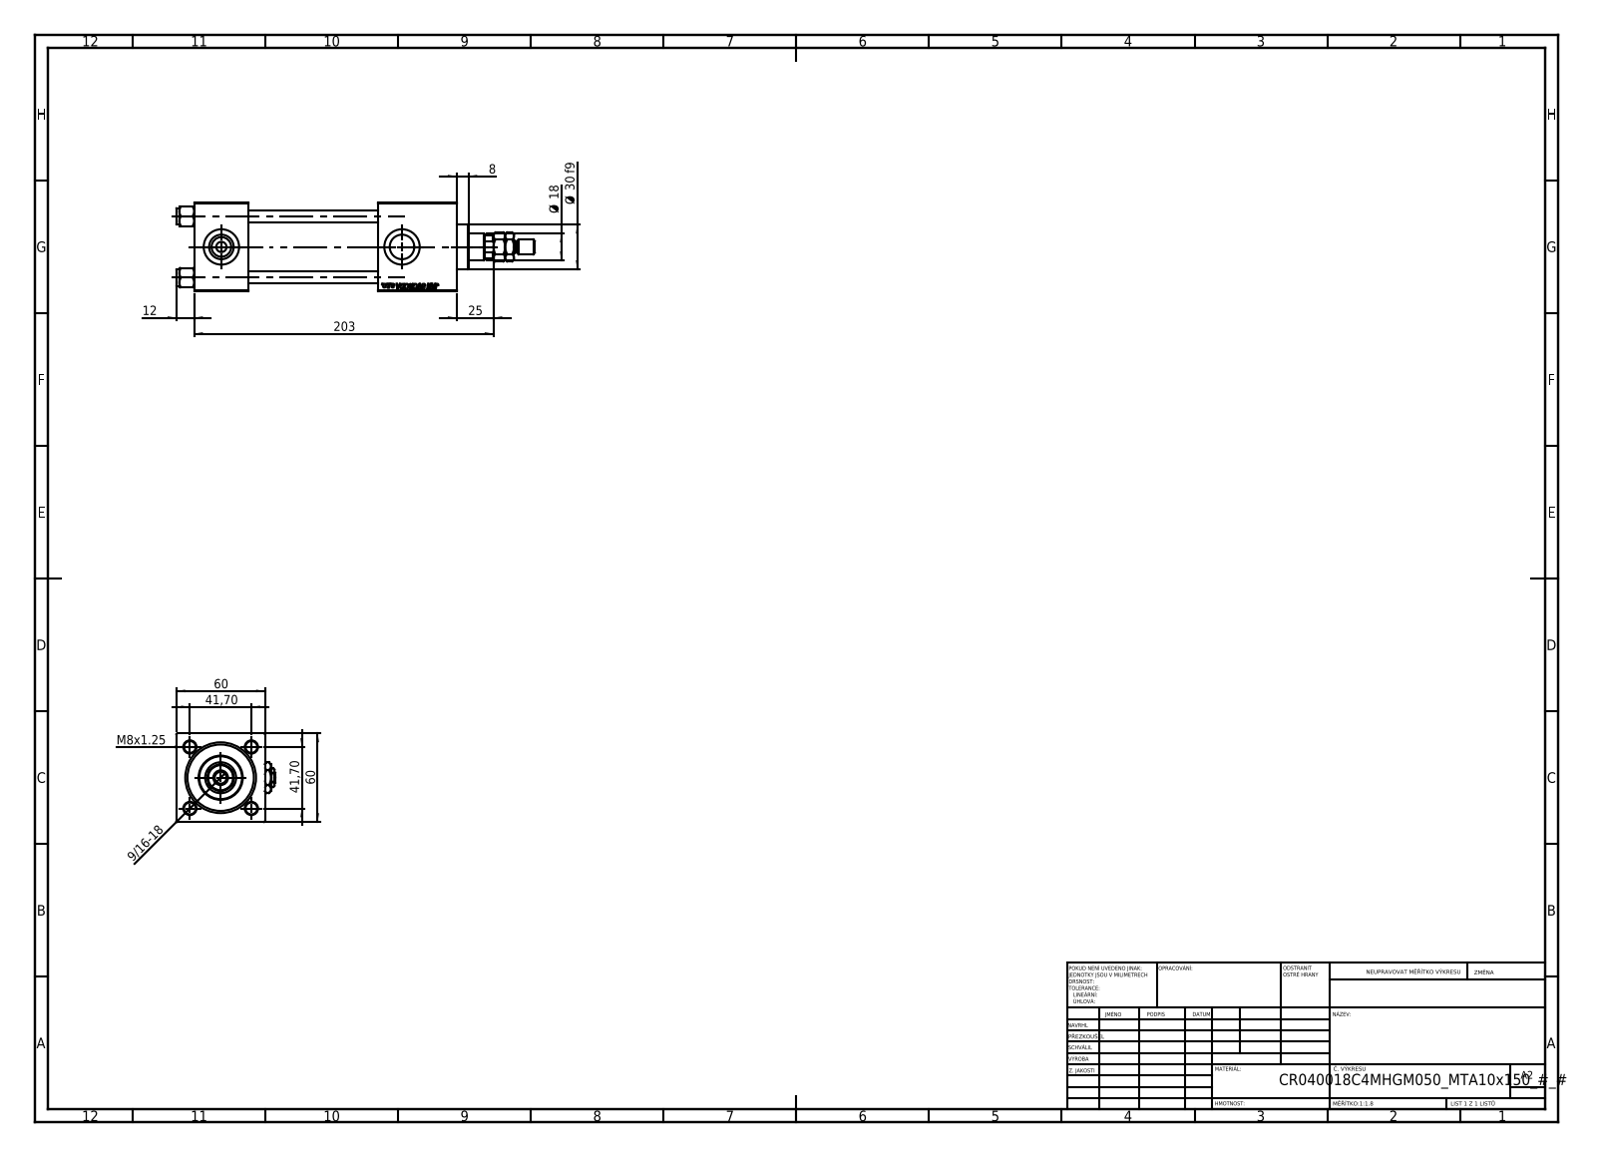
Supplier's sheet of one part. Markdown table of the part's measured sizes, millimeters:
| quantity | value |
| --- | --- |
| part name | V215CR_C_Body; MTA; V215_VC_A; Zatka_pro_OIL_PORT (+3 more) |
| STEP written by | SolidWorks 2019 (CONFIG_CONTROL_DESIGN) |
| units | millimeters |
| bodies | 13 solids, 1245 faces (565 planar, 94 cylindrical, 586 other) |
| overall size | 243 × 67 × 60 |
| volume | 430 988 mm³ |
| surface area | 121 152 mm² |
| round holes (diameter × count) | 8 × 4, 7 × 2, 16.66 × 2, 24 × 2, 8.5 × 1, 18 × 1, 21 × 1, 31 × 1, 40 × 1, 45 × 1 |
| round bosses / shafts (diameter × count) | 11 × 4, 46 × 1, 30 × 1, 10 × 1, 8 × 1 |
| partial cylindrical surfaces (radius × count) | 8.5 × 1 |
| main face-to-face distances | 60, 37, 178, 141, 53, 125, 88, 149.3, 112.3, 24.3 |
| hole center spacings | 29.49, 41.7, 58.97, 122.5 |
